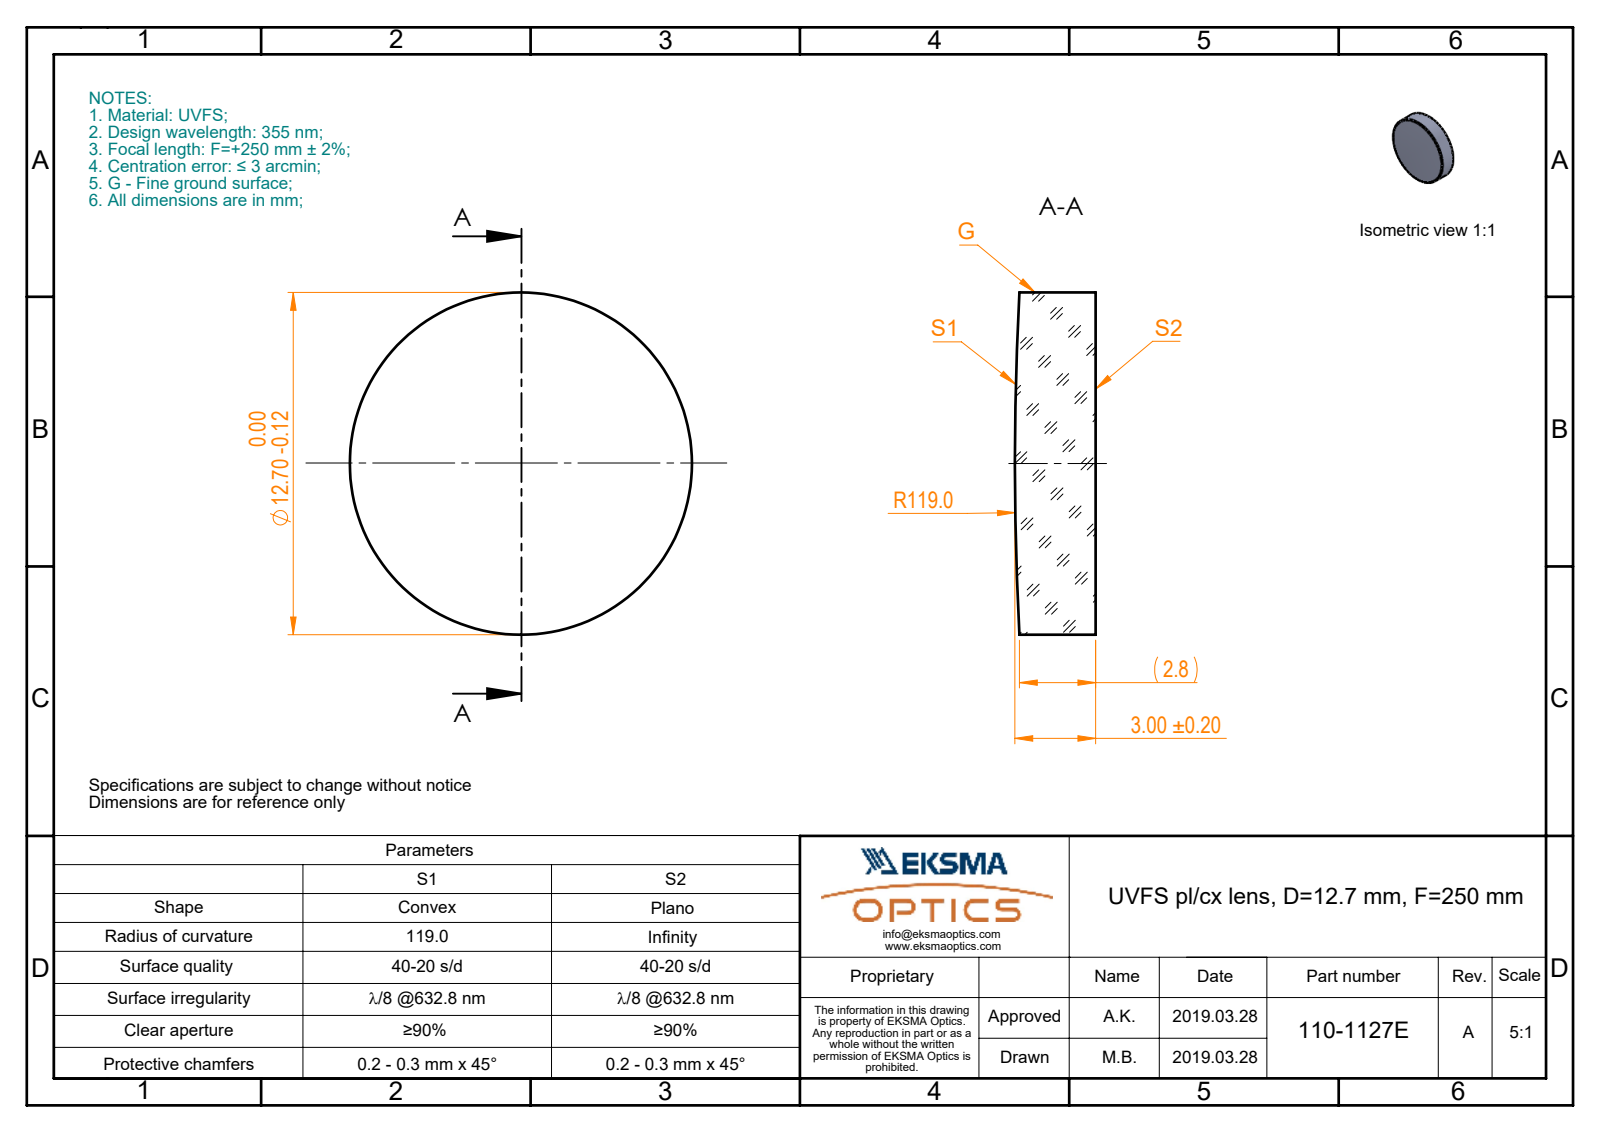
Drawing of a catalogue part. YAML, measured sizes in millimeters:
part_name: "110-1127E UVFS pl-cx 12.7 F250"
step_written_by: "SolidWorks 2017 (CONFIG_CONTROL_DESIGN)"
units: millimeters
bodies: {solids: 1, faces: 5, planar: 1, cylindrical: 2, other: 2}
overall_size: [12.7, 12.7, 3]
volume: 369
surface_area: 366
round_bosses_or_shafts:
  - {diameter: 12.7, count: 1}
